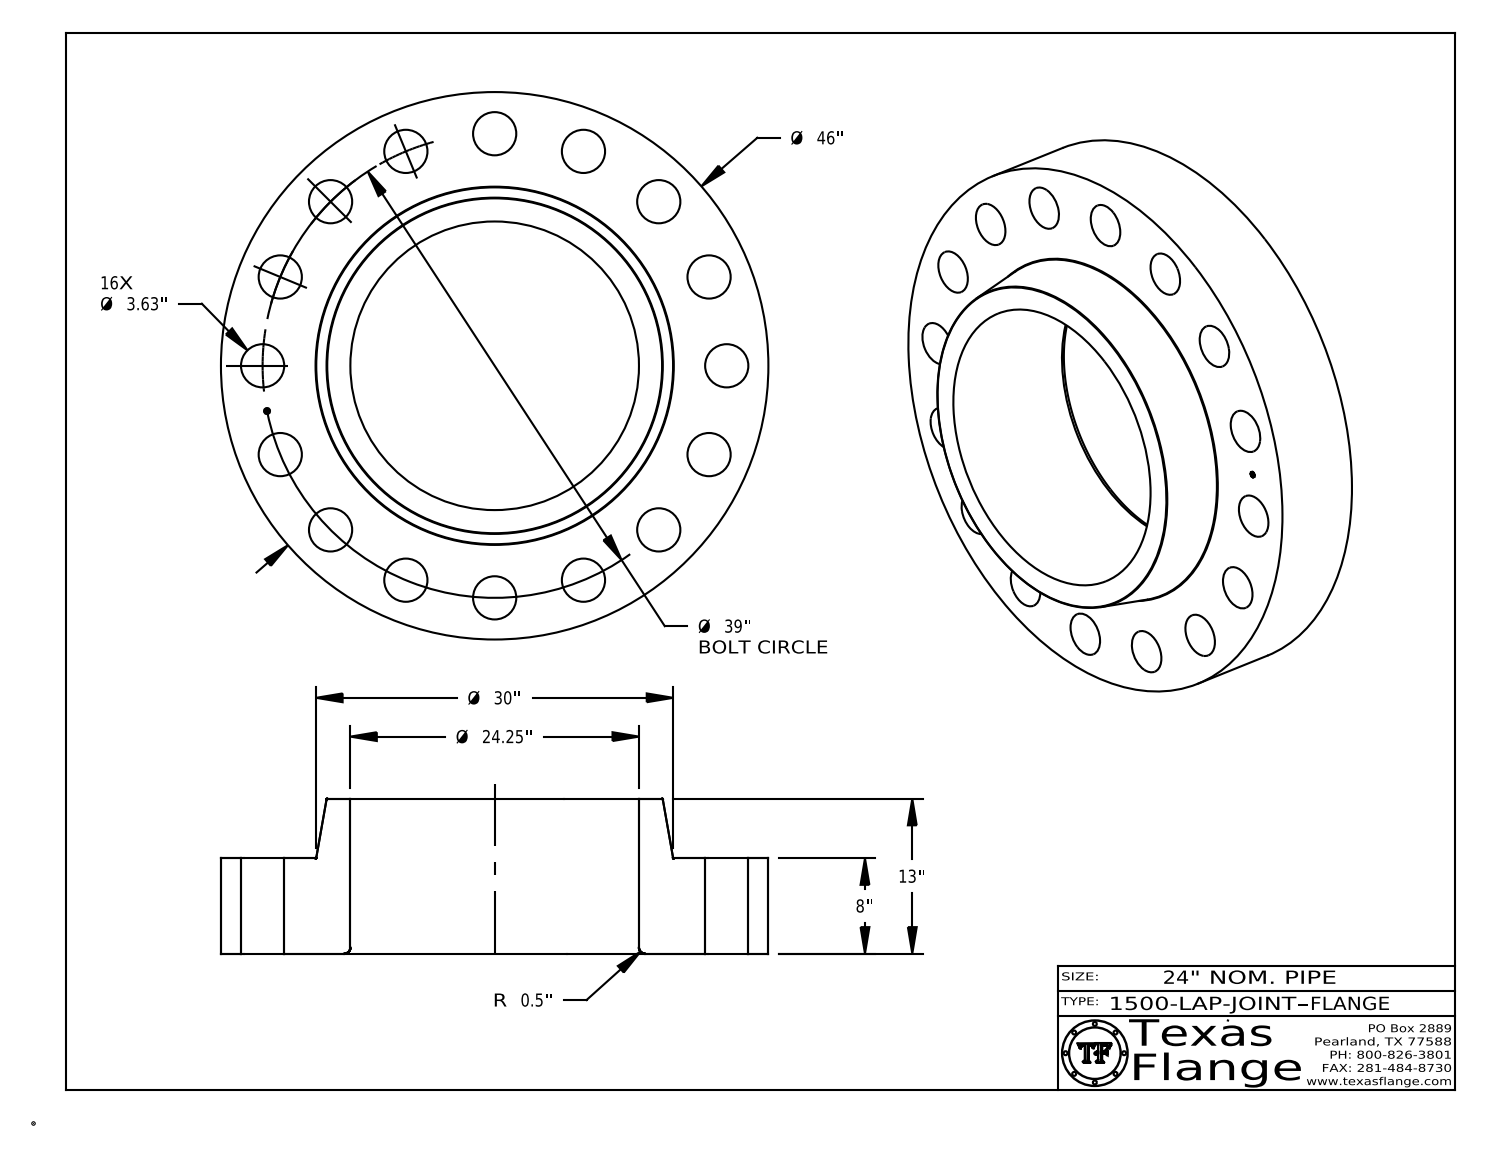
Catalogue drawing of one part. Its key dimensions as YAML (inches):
part_name: "1500-LAP-JOINT FLANGE"
step_written_by: "CATIA V5 STEP AP214 (AUTOMOTIVE_DESIGN)"
units: inches
bodies: {solids: 1, faces: 432, planar: 368, cylindrical: 56, other: 8}
overall_size: [46, 46, 13]
volume: 9293
surface_area: 6040
round_holes:
  - {diameter: 3.63, count: 16}
  - {diameter: 0.495, count: 1}
  - {diameter: 24.25, count: 1}
round_bosses_or_shafts:
  - {diameter: 0.03, count: 8}
  - {diameter: 46, count: 1}
  - {diameter: 0.39, count: 1}
face_to_face_distances: [8, 13, 5, 7.985, 0.015, 5.015, 0.148, 0.145, 0.027, 0.096]
hole_center_spacings: [19.5, 21.667, 27.577, 38.251, 14.925, 36.031, 7.608, 7.609]
